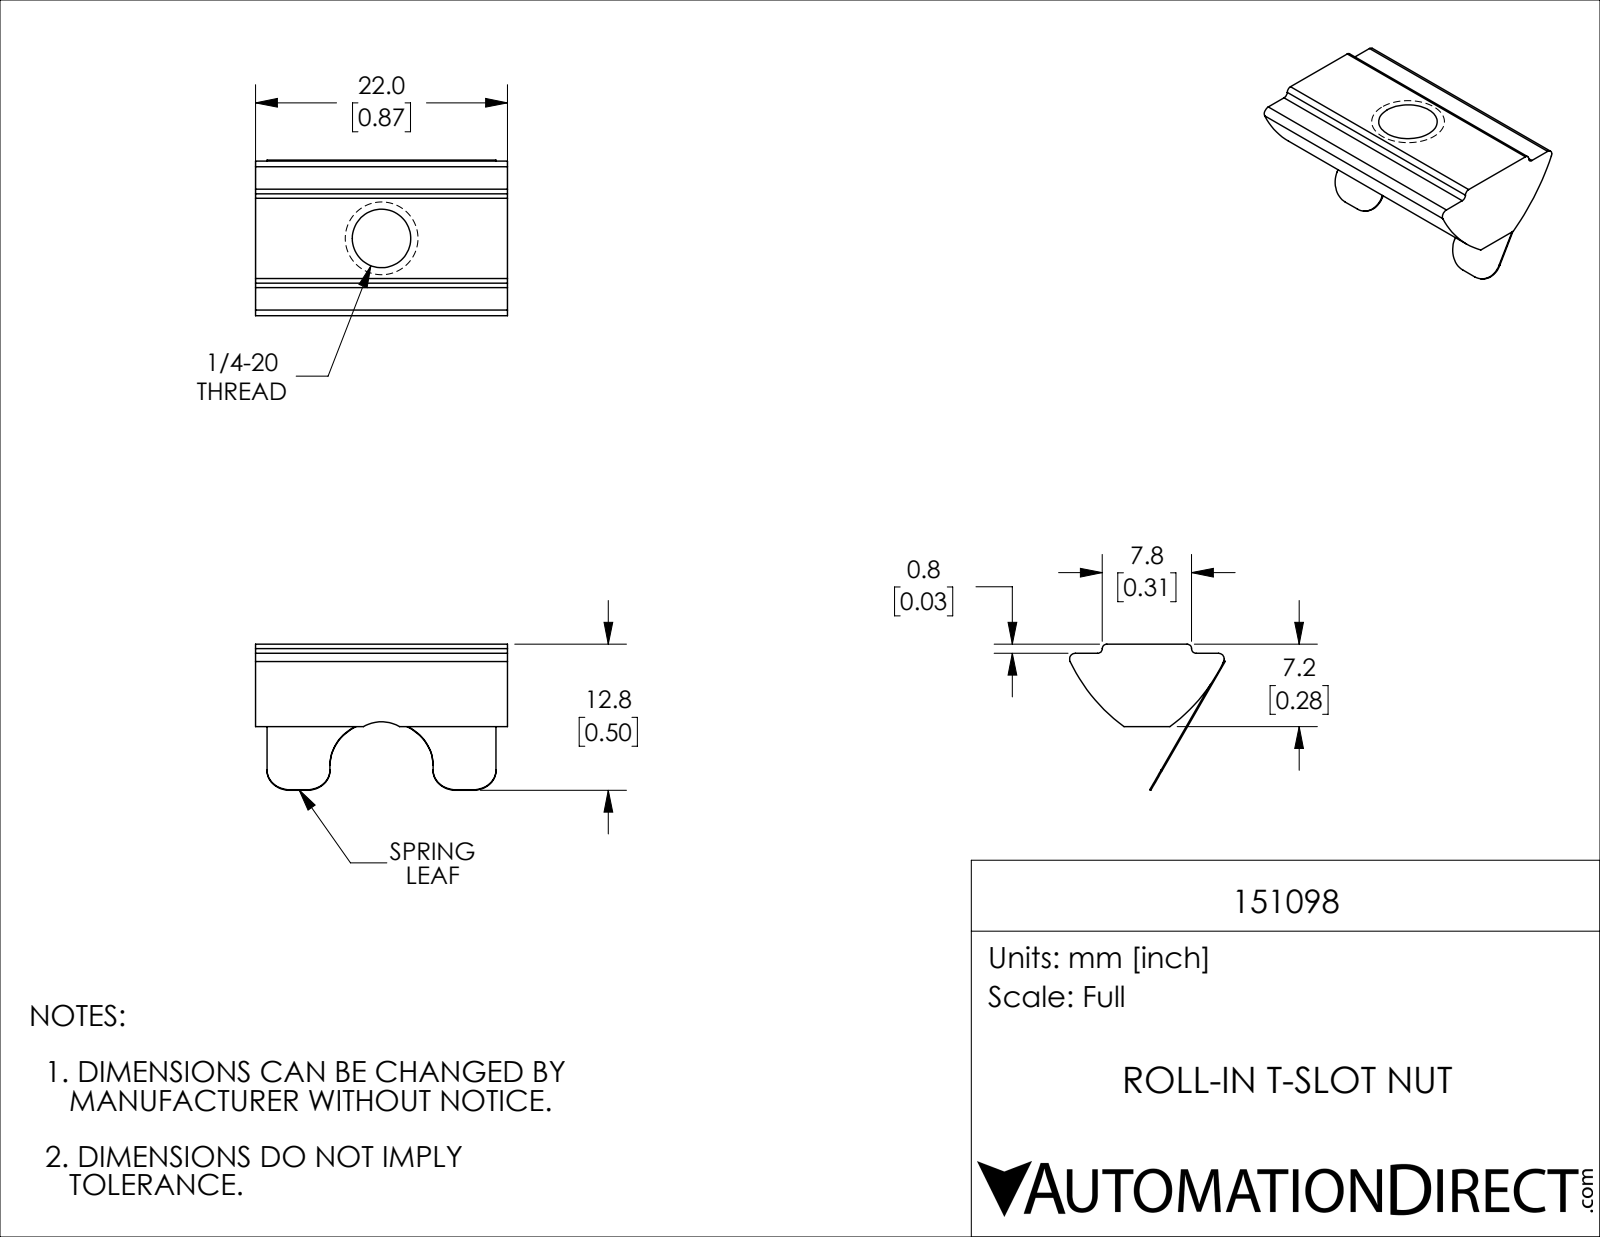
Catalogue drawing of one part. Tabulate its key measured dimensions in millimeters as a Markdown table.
| quantity | value |
| --- | --- |
| part name | 151098 |
| STEP written by | SolidWorks 2021 (CONFIG_CONTROL_DESIGN) |
| units | millimeters |
| bodies | 1 solid, 33 faces (17 planar, 16 cylindrical, 0 other) |
| overall size | 22 × 13.59 × 12.76 |
| volume | 1 407 mm³ |
| surface area | 1 291 mm² |
| round holes (diameter × count) | 5.11 × 1 |
| partial cylindrical surfaces (radius × count) | 0.4 × 4, 2 × 4, 0.5 × 2, 15 × 2, 4.5 × 1 |
| main face-to-face distances | 0.8, 6.4, 7.2, 22, 1, 21, 20, 13, 6.5, 15.5 |
